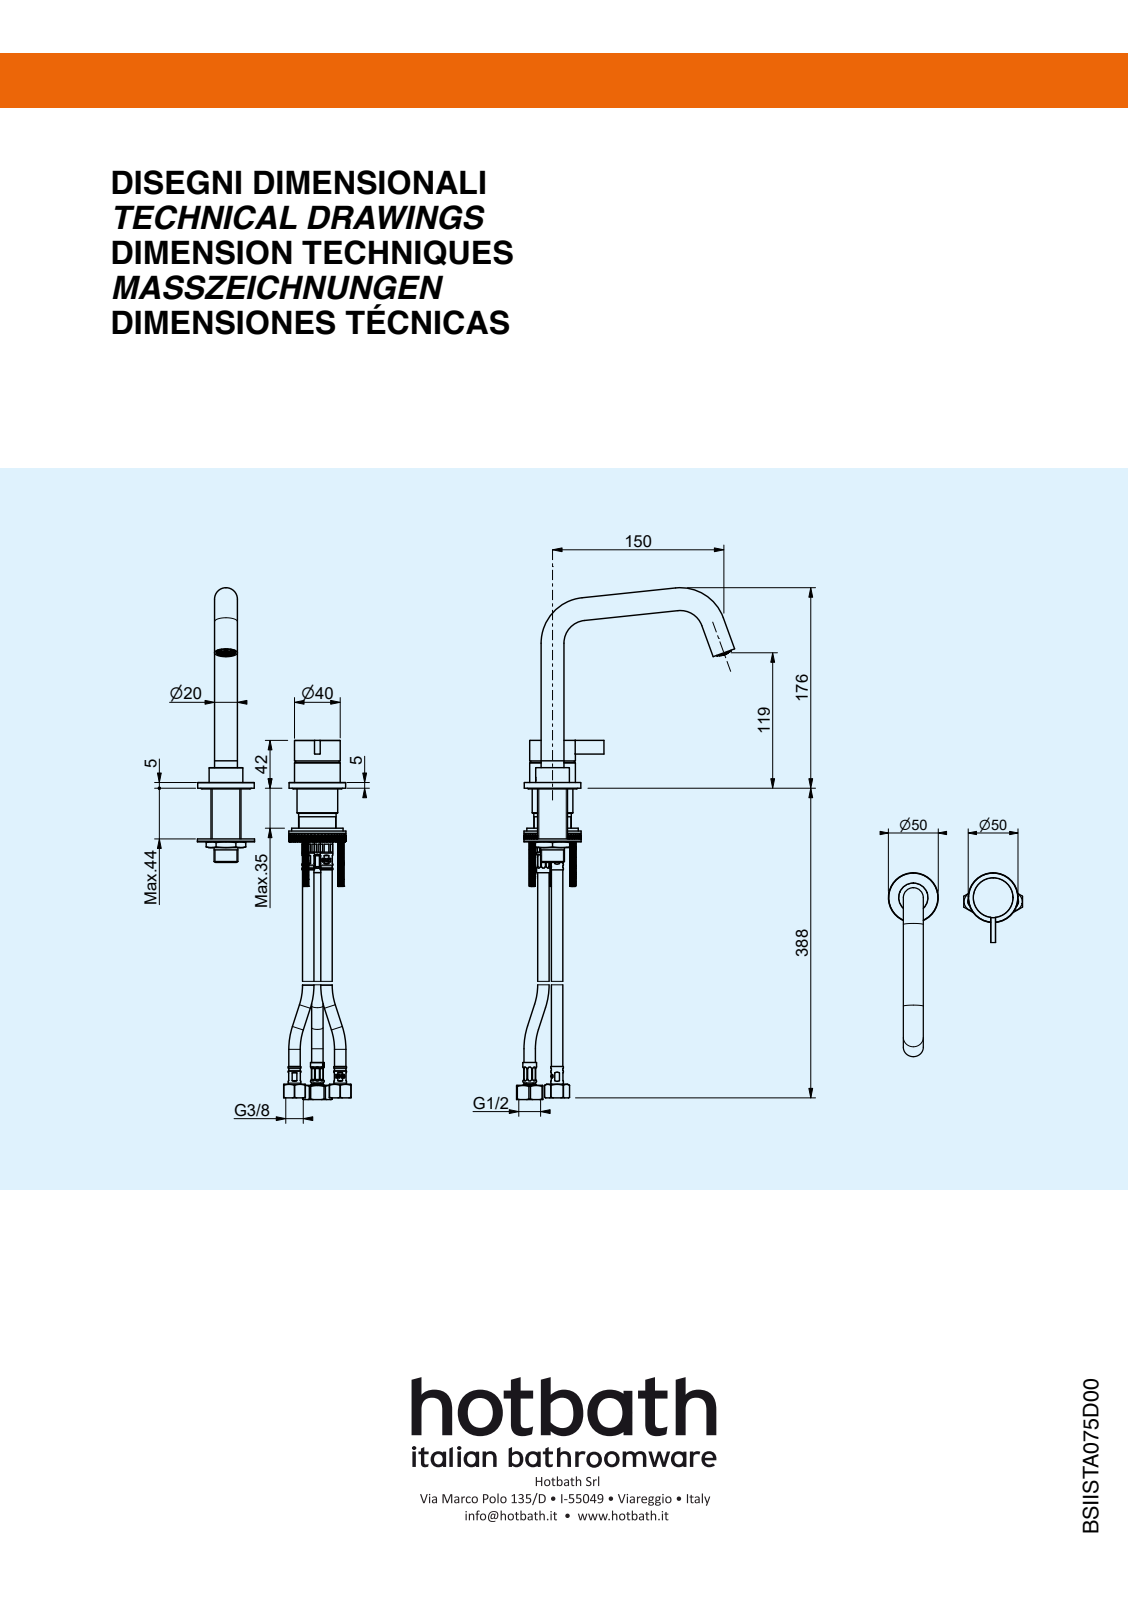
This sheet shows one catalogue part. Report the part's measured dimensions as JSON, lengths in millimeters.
{"part_name": "AF023-00; BSIMVXA060_1_oa_0; SBTBSC0003_oa_1; ABIX112C001_oa_2 (+8 more)", "step_written_by": "Solid Edge (AUTOMOTIVE_DESIGN)", "units": "millimeters", "bodies": {"solids": 9, "faces": 2777, "planar": 1877, "cylindrical": 304, "other": 596}, "overall_size": [184.15, 175.61, 159.5], "volume_mm3": 83736, "surface_area_mm2": 67366, "round_holes": [[2.5, 3], [15, 3], [44.5, 2], [3.2, 1], [9, 1], [11, 1], [12.15, 1], [12.45, 1], [13.55, 1], [14.55, 1], [15.5, 1], [16.7, 1]], "round_bosses_or_shafts": [[20, 3], [0.9, 3], [49.5, 2], [34.5, 2], [38, 1], [37.3, 1], [35.6, 1], [29.5, 1]], "partial_cylinders_radius": [[0.1, 58], [0.2, 8], [0.9, 8], [0.25, 4], [0.4, 4], [0.6, 4], [1.27, 4], [1.3, 4]], "face_to_face_distances": [5, 2, 41.9, 36.9, 3, 39.9, 4.6, 37.3, 35.3, 32.3], "hole_center_spacings": [12, 13.5, 25.5, 110, 110.65, 110.83]}
